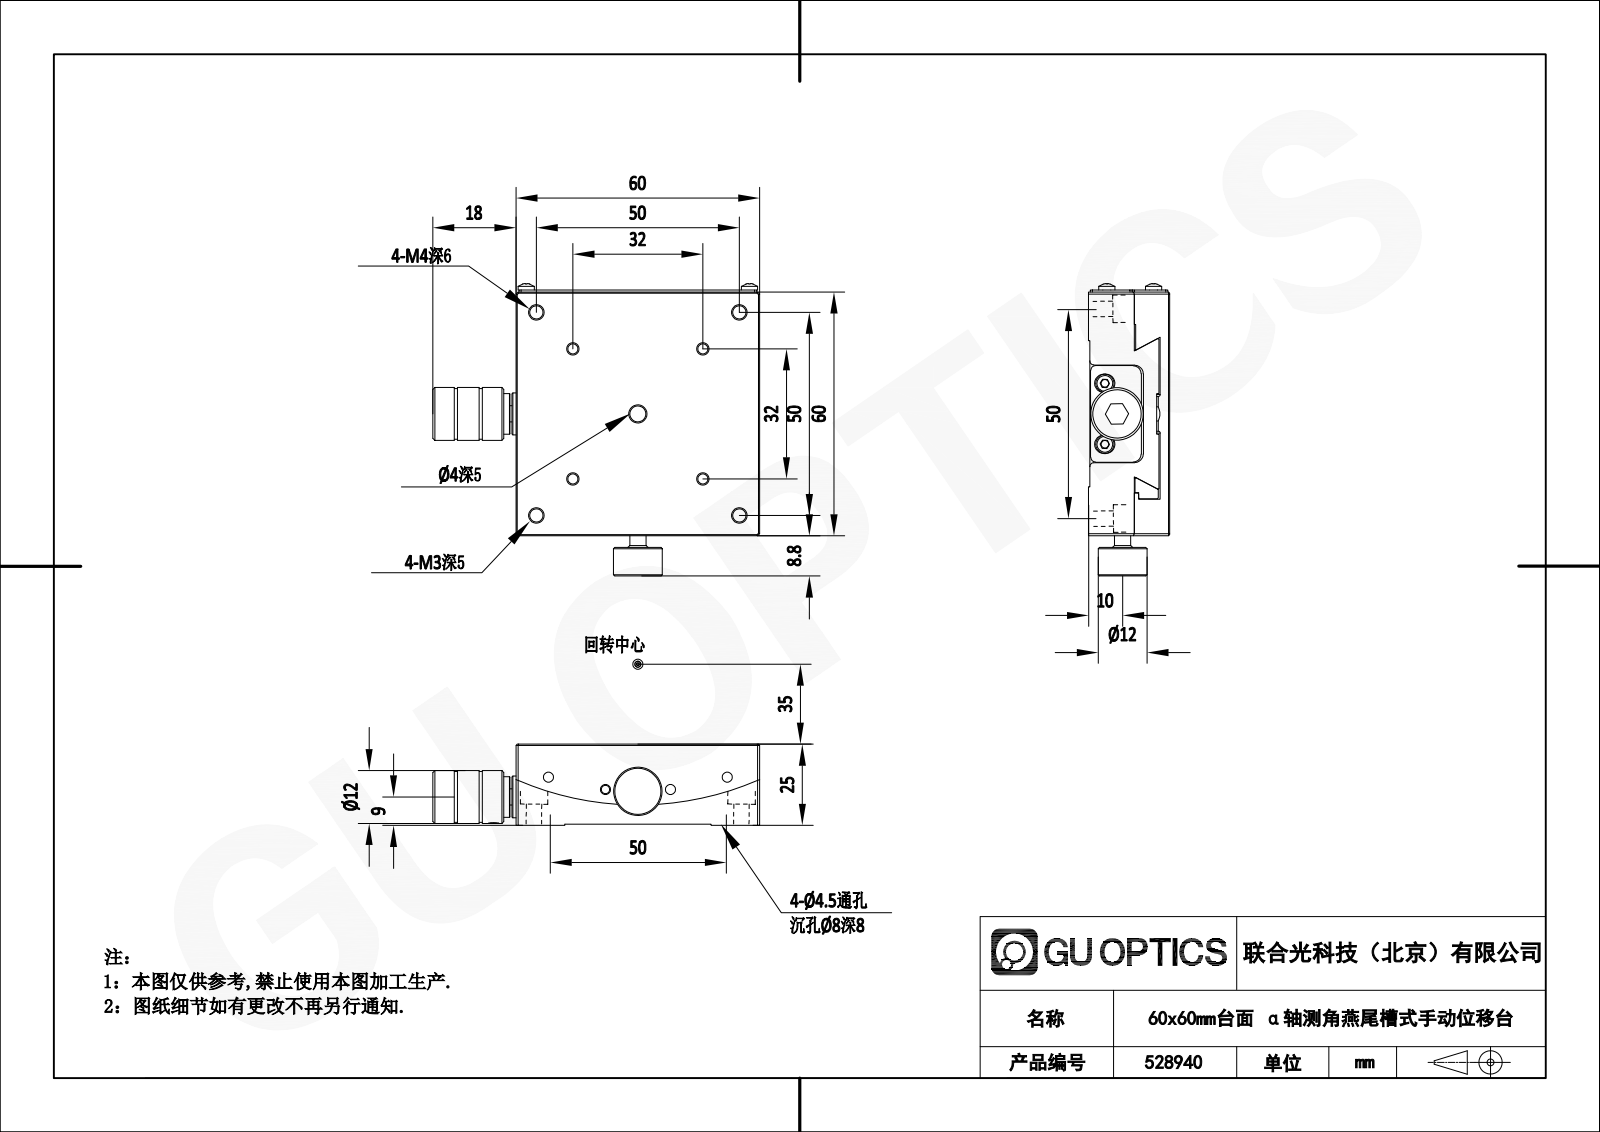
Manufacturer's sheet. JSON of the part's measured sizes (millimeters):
{"part_name": "528940", "step_written_by": "SolidWorks 2020 (CONFIG_CONTROL_DESIGN)", "units": "millimeters", "bodies": {"solids": 22, "faces": 2178, "planar": 1204, "cylindrical": 573, "other": 401}, "overall_size": [79.95, 73.08, 25], "volume_mm3": 87174, "surface_area_mm2": 39061, "round_holes": [[2.5, 9], [2.1, 5], [3.3, 5], [1.6, 4], [4.5, 4], [8, 4], [2.05, 2], [4, 2], [10, 1], [11, 1], [12, 1]], "round_bosses_or_shafts": [[4, 5], [2, 4], [4.5, 2], [2.5, 2], [10.3, 1], [9, 1], [6.5, 1], [3, 1]], "partial_cylinders_radius": [[0.3, 18], [0.5, 8], [1.4, 4], [2.3, 4], [53, 3], [3.1, 2], [3.5, 2], [4.25, 2]], "face_to_face_distances": [24.7, 60, 0.5, 60.5, 6.25, 53.75, 40.5, 19.5, 25, 53.7], "hole_center_spacings": [41.98, 12.73, 22.63, 32, 35.36, 50, 57.98, 5.89]}
